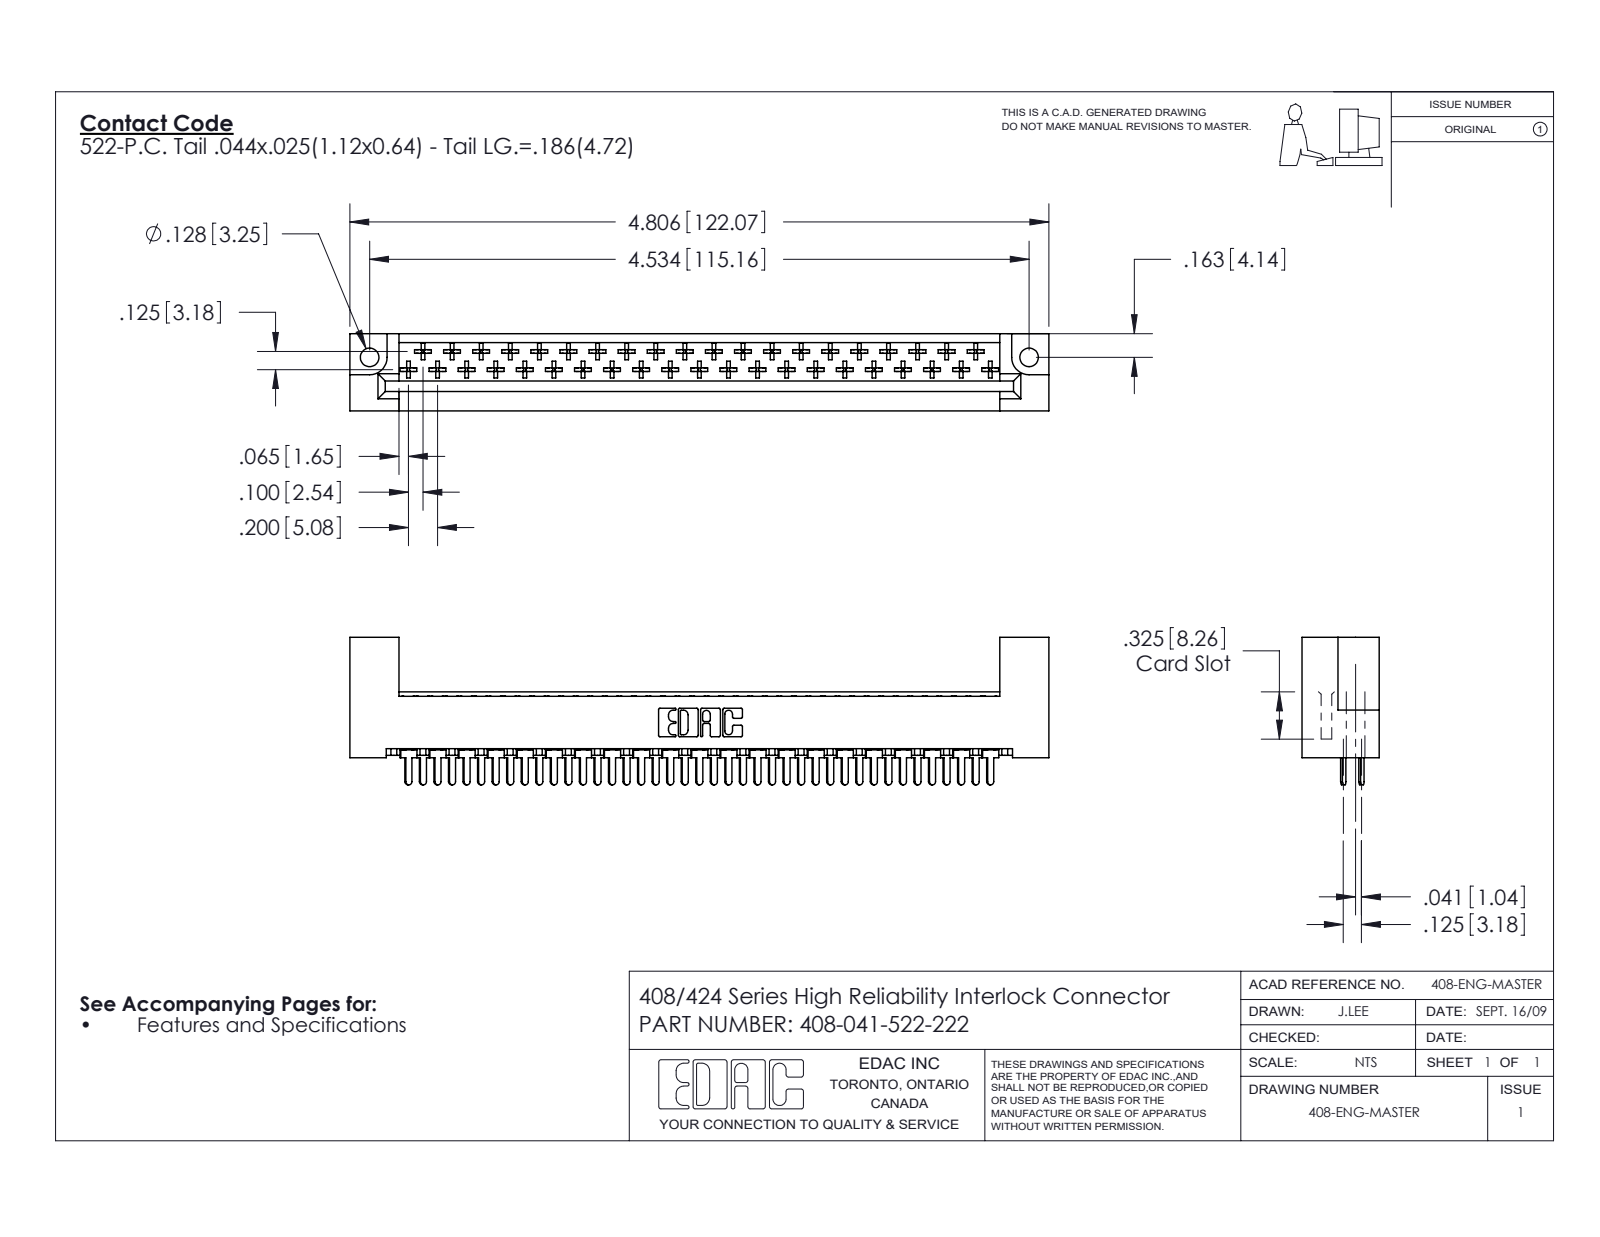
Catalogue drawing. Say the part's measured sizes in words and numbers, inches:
The part is named "408-047-522-222; 408-290-001_408-290-122; 408 Part_041 - 2". Its 3-D file was written by "SolidWorks 2016 (CONFIG_CONTROL_DESIGN)". It is 42 solids with 2394 faces: 1811 planar, 419 cylindrical and 164 other. Overall it measures 4.806 by 1.014 by 0.531 inches. Its volume is 0.919 cubic inches and its surface area 27.49 square inches. Round holes: 2 of diameter 0.128. Partial cylindrical surfaces (rounded edges, fillets, slot ends): 246 of radius 0.01, 43 of radius 0.02, 41 of radius 0.022, 22 of radius 0.01, 6 of radius 0.007, 6 of radius 0.031, 3 of radius 0.026, 2 of radius 0.12. The main face-to-face distances are 0.531, 0.125, 0.1, 0.025, 0.025, 0.361, 0.235, 0.259, 0.398, 0.217. The hole center spacings are 4.534.
